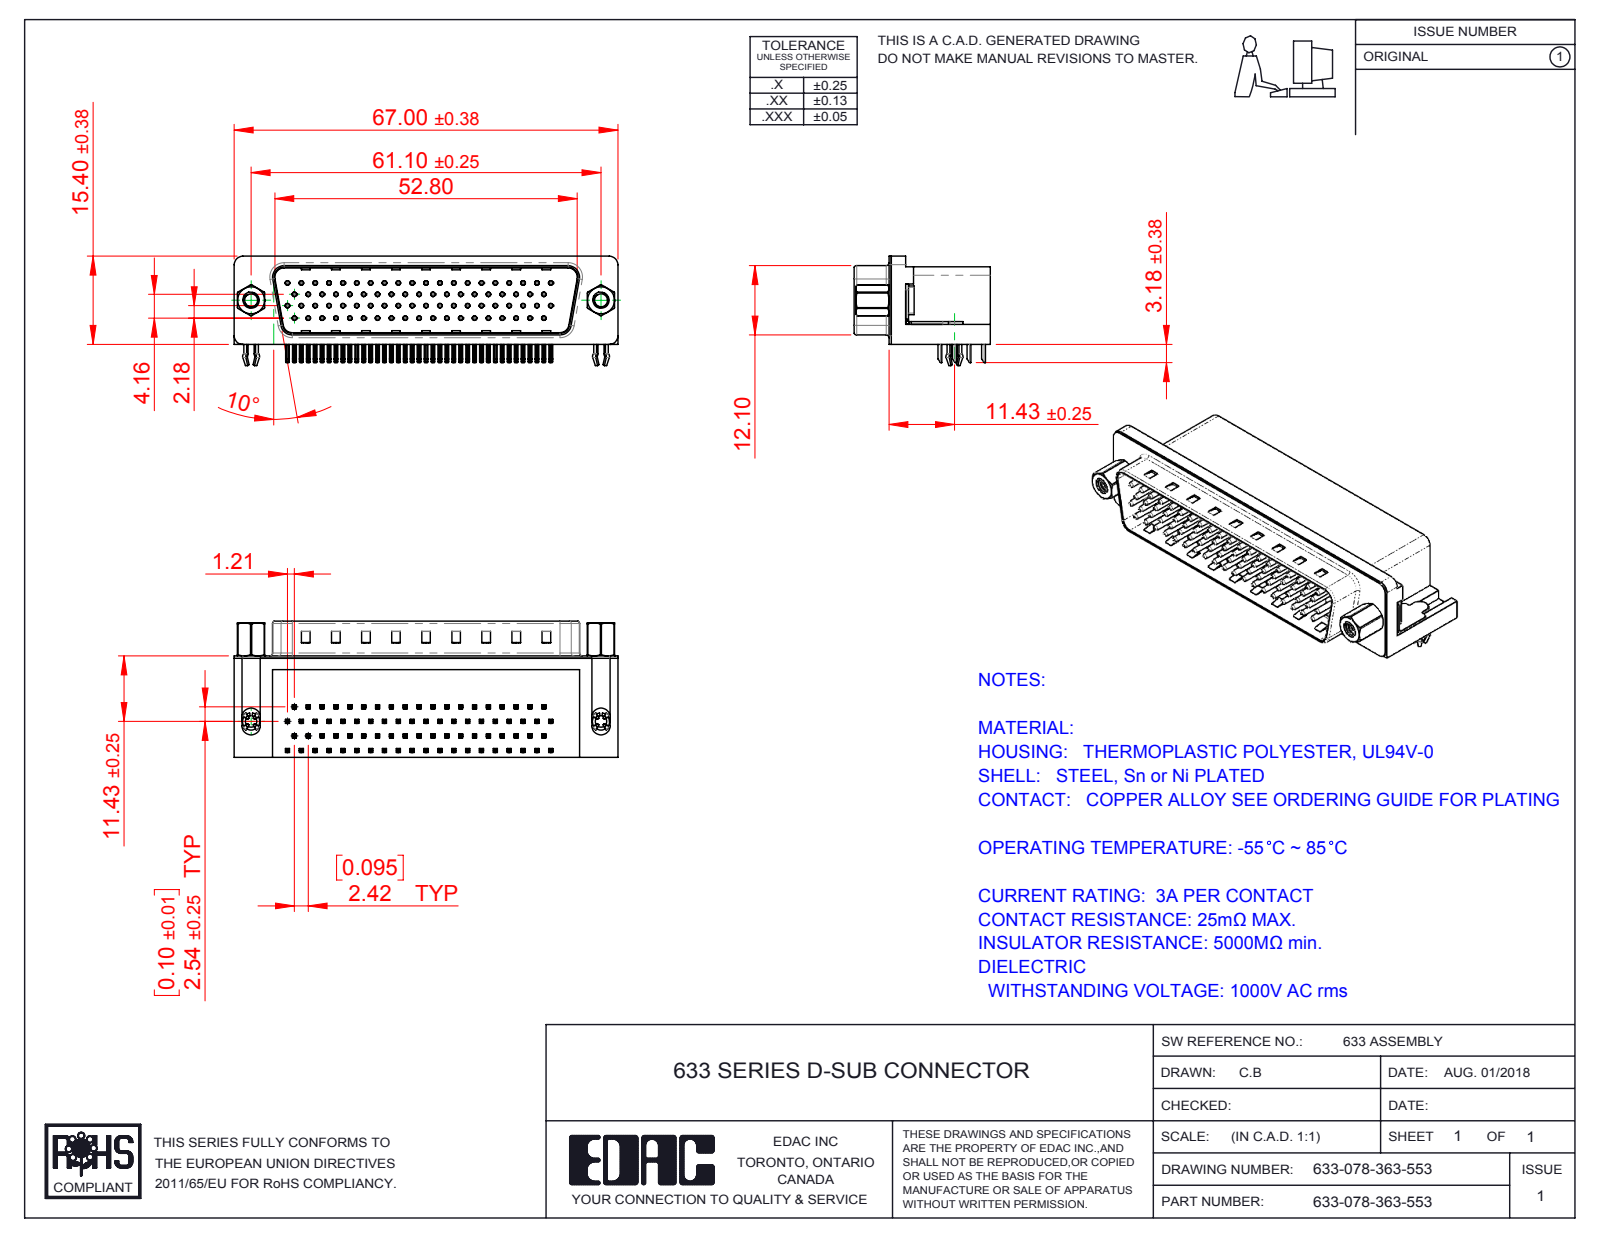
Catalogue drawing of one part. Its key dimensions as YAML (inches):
part_name: "633-078-363-553; 633 4-40 Hex Standoff; 633 4-40 Threaded Rivet; 633 4 Prong Board Lock_78 Contact (+6 more)"
step_written_by: "SolidWorks 2016 (CONFIG_CONTROL_DESIGN)"
units: inches
bodies: {solids: 86, faces: 6516, planar: 4045, cylindrical: 1848, other: 623}
overall_size: [2.638, 0.937, 0.752]
volume: 0.905
surface_area: 26.17
round_holes:
  - {diameter: 0.014, count: 78}
  - {diameter: 0.031, count: 78}
  - {diameter: 0.079, count: 2}
  - {diameter: 0.089, count: 2}
  - {diameter: 0.09, count: 2}
  - {diameter: 0.157, count: 2}
  - {diameter: 0.189, count: 2}
  - {diameter: 0.197, count: 2}
round_bosses_or_shafts:
  - {diameter: 0.03, count: 78}
  - {diameter: 0.193, count: 2}
  - {diameter: 0.187, count: 2}
  - {diameter: 0.154, count: 2}
  - {diameter: 0.118, count: 2}
  - {diameter: 0.11, count: 2}
partial_cylinders:
  - {radius: 0.01, count: 324}
  - {radius: 0.005, count: 156}
  - {radius: 0.039, count: 16}
  - {radius: 0.02, count: 9}
  - {radius: 0.063, count: 8}
  - {radius: 0.059, count: 6}
  - {radius: 0.018, count: 4}
  - {radius: 0.035, count: 4}
face_to_face_distances: [0.016, 0.52, 0.681, 0.461, 0.526, 0.081, 0.541, 0.065, 0.073, 0.469]
hole_center_spacings: [0.095, 0.191, 0.286, 0.381, 0.246, 0.281, 0.476, 0.339]
